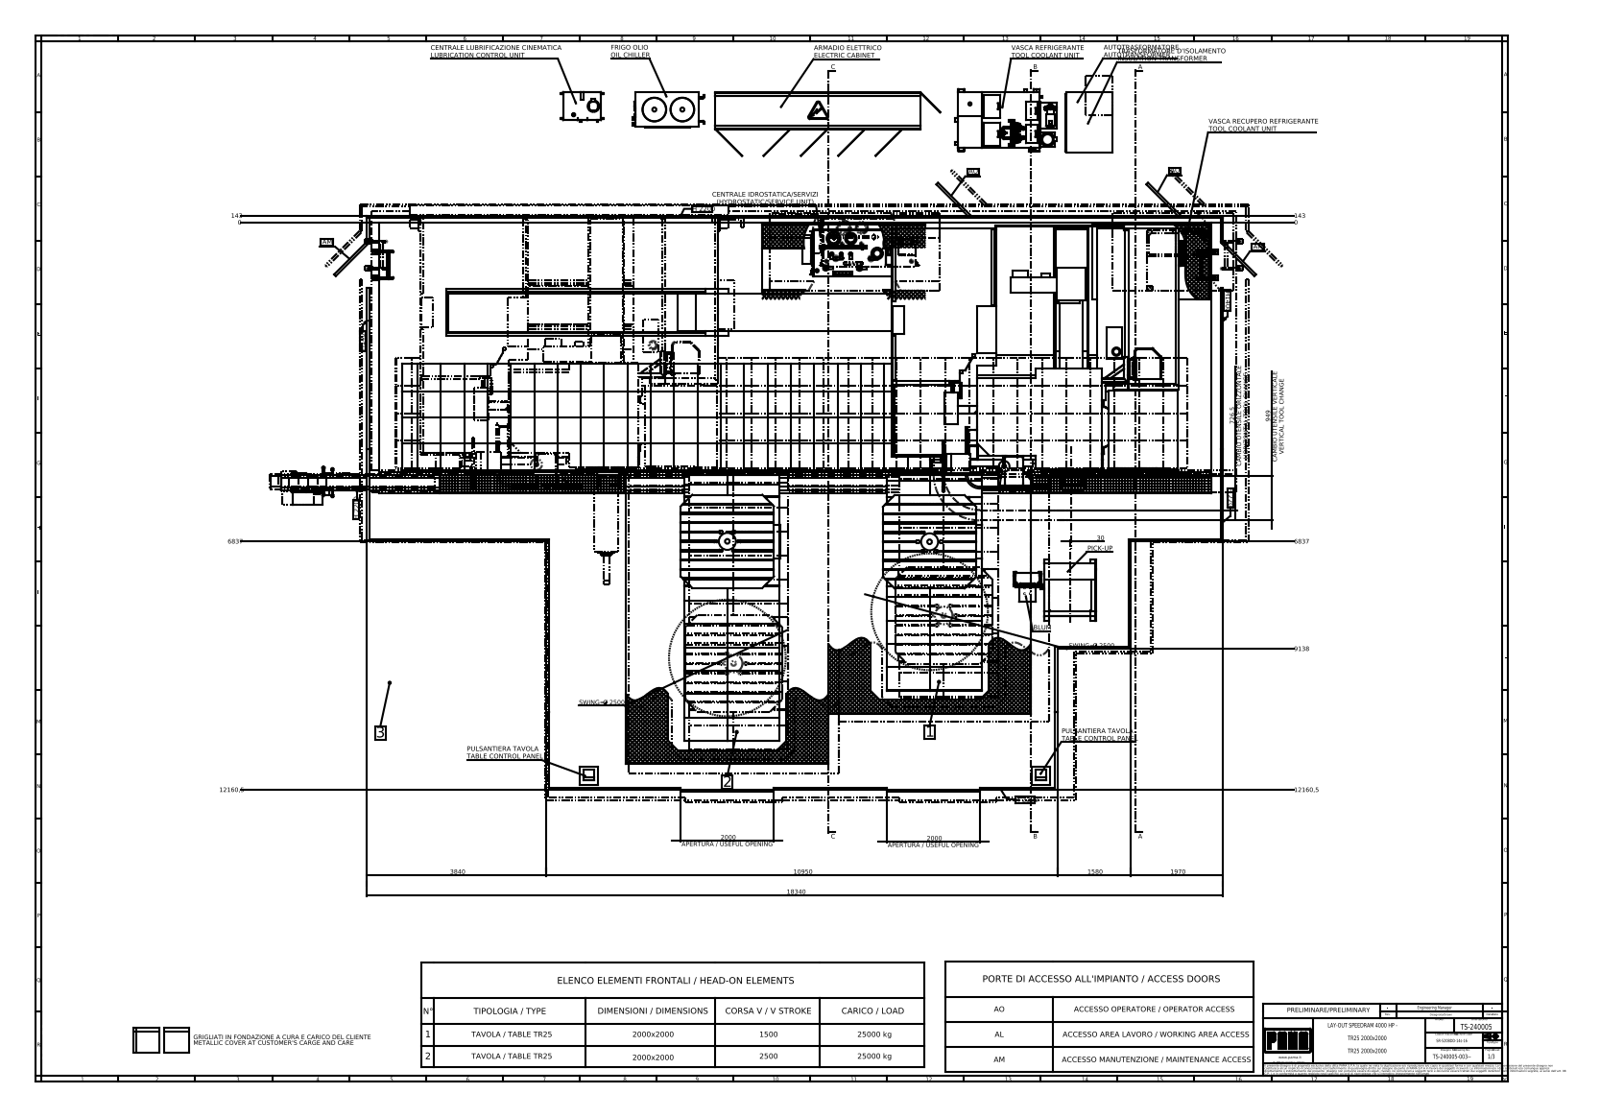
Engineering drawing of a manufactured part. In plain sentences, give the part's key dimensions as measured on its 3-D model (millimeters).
The part is named "S001571; S002117_CORSA V=0; B=0°; S003233_NO CARTERATURA; S001796 (+8 more)". Its 3-D file was written by "SolidWorks 2023 (AUTOMOTIVE_DESIGN)". It is 498 solids with 8588 faces: 6264 planar, 1769 cylindrical and 555 other. Overall it measures 21840 by 17974.9 by 10949 millimeters. Its volume is 669 100 000 000 cubic millimeters and its surface area 2 497 000 000 square millimeters. Round holes: 144 of diameter 35, 63 of diameter 69.6, 18 of diameter 37.2, 9 of diameter 30, 8 of diameter 13, 8 of diameter 14, 6 of diameter 8, 4 of diameter 12.5, 4 of diameter 56.66, 4 of diameter 60, 3 of diameter 25.6, 3 of diameter 50. Round bosses or shafts: 18 of diameter 42.4, 14 of diameter 20, 11 of diameter 40, 10 of diameter 9, 8 of diameter 55, 7 of diameter 66.3, 6 of diameter 60, 6 of diameter 35. Partial cylindrical surfaces (rounded edges, fillets, slot ends): 136 of radius 5, 57 of radius 15, 56 of radius 8, 28 of radius 10, 26 of radius 35, 25 of radius 6, 24 of radius 25, 21 of radius 3. The main face-to-face distances are 2000, 50, 720, 1280, 10, 1152.8, 432.8, 847.2, 17903.5, 2650. The hole center spacings are 273.13, 500, 1431.99, 758.02, 1597.06, 1000, 130, 260.
